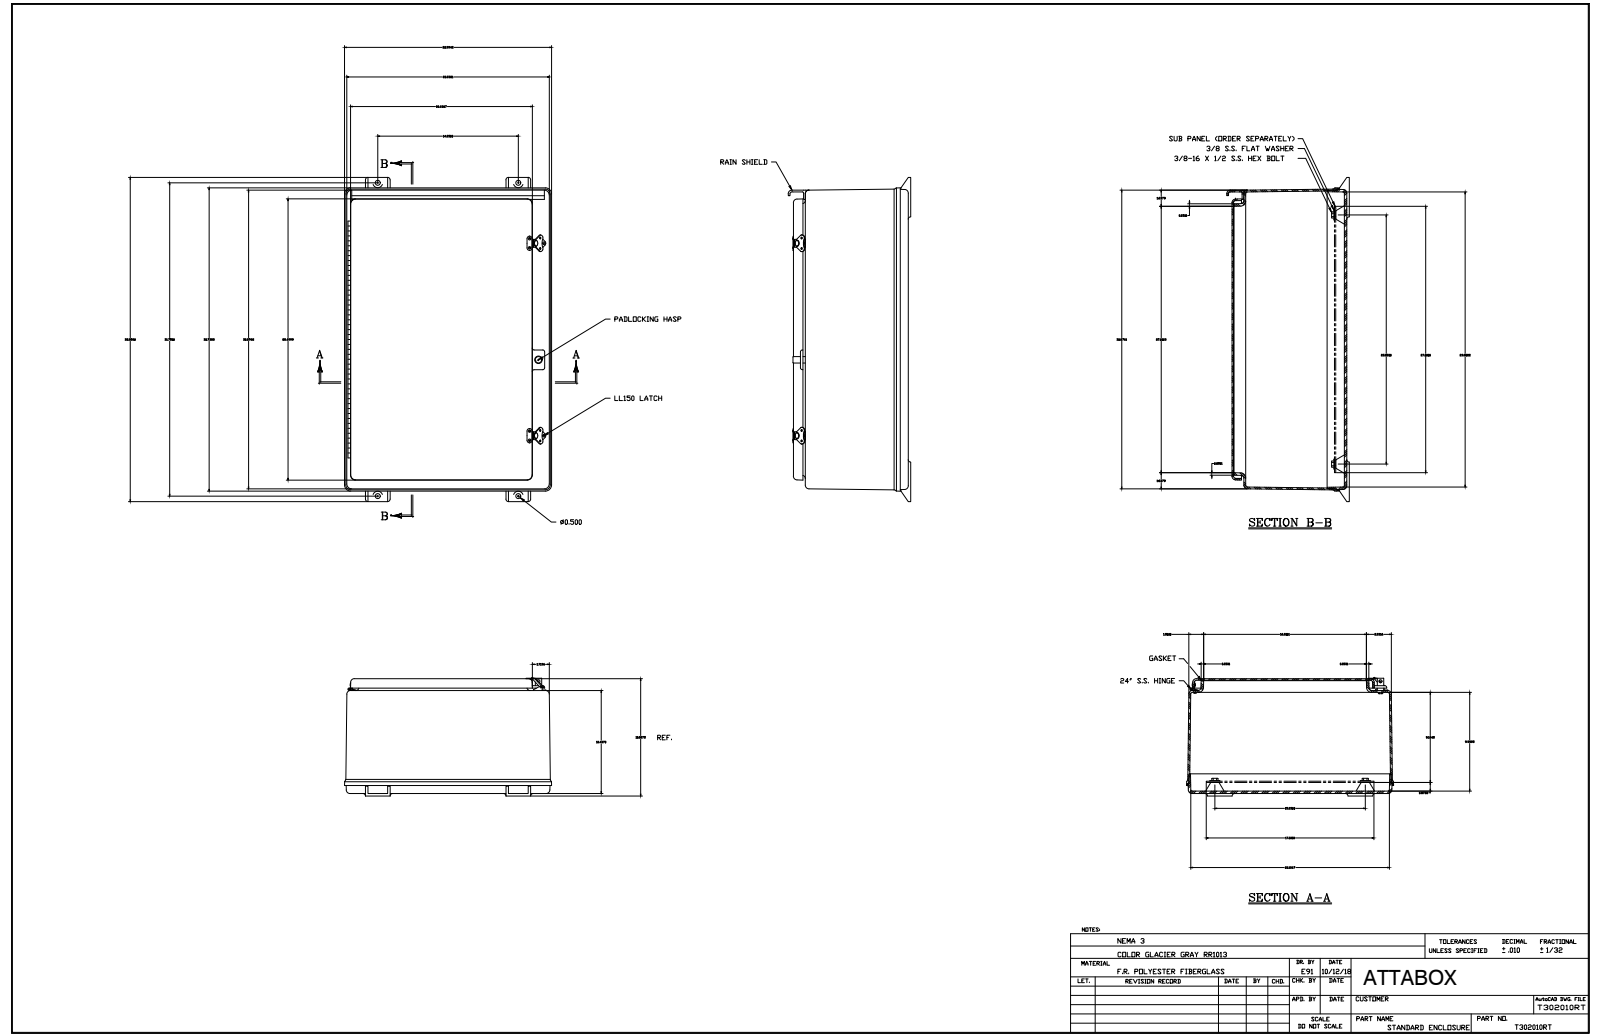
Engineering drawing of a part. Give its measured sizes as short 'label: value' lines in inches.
name: T302010RT
written by: SolidWorks 2018 (AUTOMOTIVE_DESIGN)
unit: in
bodies: 40 solids, 1199 faces (475 planar, 476 cylindrical, 248 other)
size: 32.844 × 21 × 12.438
volume: 530 in³; area: 5 611 in²
holes: 25× ⌀0.13, 8× ⌀0.063, 6× ⌀0.065, 5× ⌀0.065, 4× ⌀0.138, 4× ⌀0.187, 4× ⌀0.563, 2× ⌀0.51, 2× ⌀0.51, 1× ⌀0.125, 1× ⌀0.125, 1× ⌀0.135
bosses: 11× ⌀0.297, 8× ⌀0.14, 2× ⌀0.5, 1× ⌀0.25, 1× ⌀0.201, 1× ⌀0.2, 1× ⌀0.135
rounds: 60× R0.01, 24× R0.25, 14× R0.187, 12× R0.375, 12× R0.5, 9× R0.313, 8× R0.03, 8× R0.188
face distances: 0.187, 0.25, 0.156, 11.625, 11.375, 11.469, 11.219, 1.187, 10.437, 10.25
hole spacings: 19.5, 0.938, 1.542, 7.5, 15.5, 0.858, 0.858, 6.612
